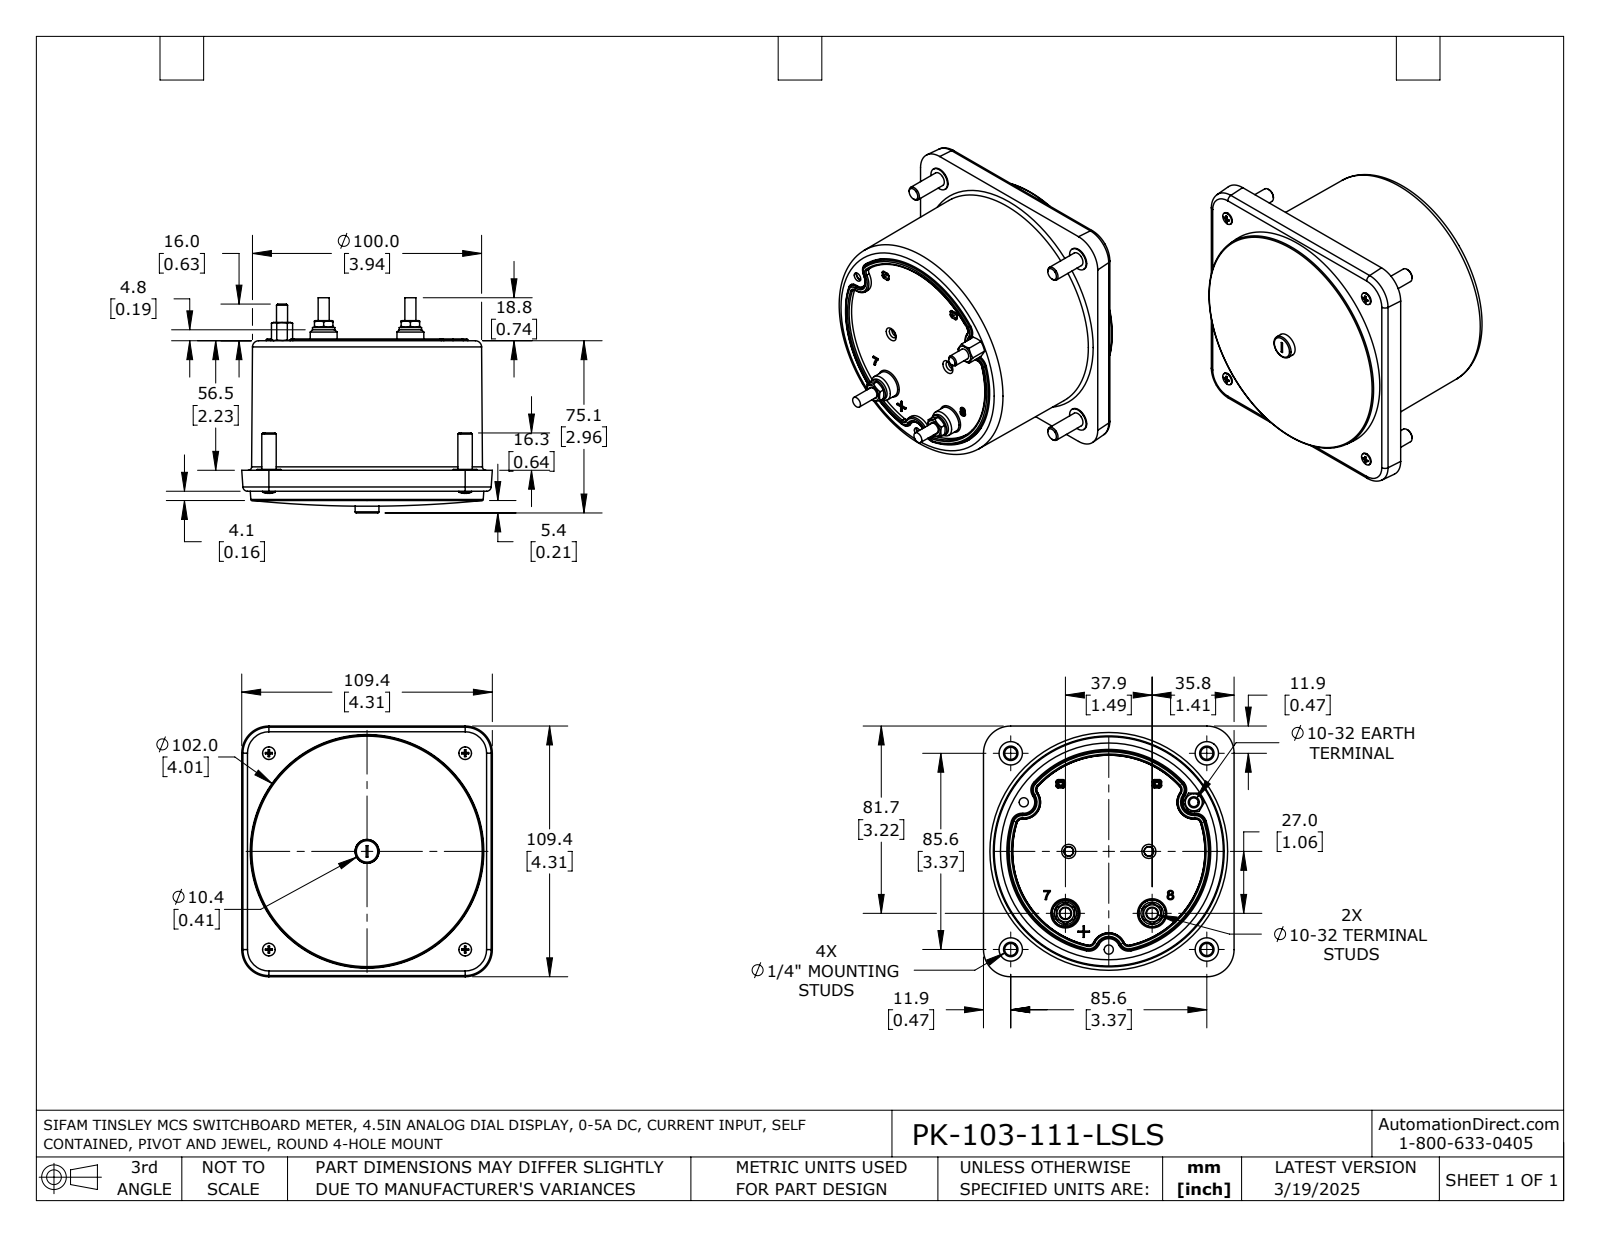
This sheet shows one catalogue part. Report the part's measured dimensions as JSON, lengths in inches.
{"part_name": "PK-103-111-LSLS", "step_written_by": "SolidWorks 2021 (AUTOMOTIVE_DESIGN)", "units": "inches", "bodies": {"solids": 1, "faces": 609, "planar": 167, "cylindrical": 141, "other": 301}, "overall_size": [4.307, 4.307, 3.697], "volume_in3": 36.28, "surface_area_in2": 82.21, "round_holes": [[0.094, 4], [0.138, 4], [0.315, 4], [0.157, 3], [0.209, 2]], "round_bosses_or_shafts": [[0.402, 4], [0.248, 4], [0.217, 4], [0.114, 4], [0.19, 3], [0.384, 2], [0.146, 1]], "partial_cylinders_radius": [[0.02, 24], [0.189, 9], [0.079, 4], [1.752, 1]], "face_to_face_distances": [2.177, 2.537, 0.36, 0.048, 2.225, 2.585, 0.489, 2.715, 2.667, 0.129], "hole_center_spacings": [3.372, 3.37, 3.374, 3.378, 3.38, 4.769, 0.971, 1.126]}
